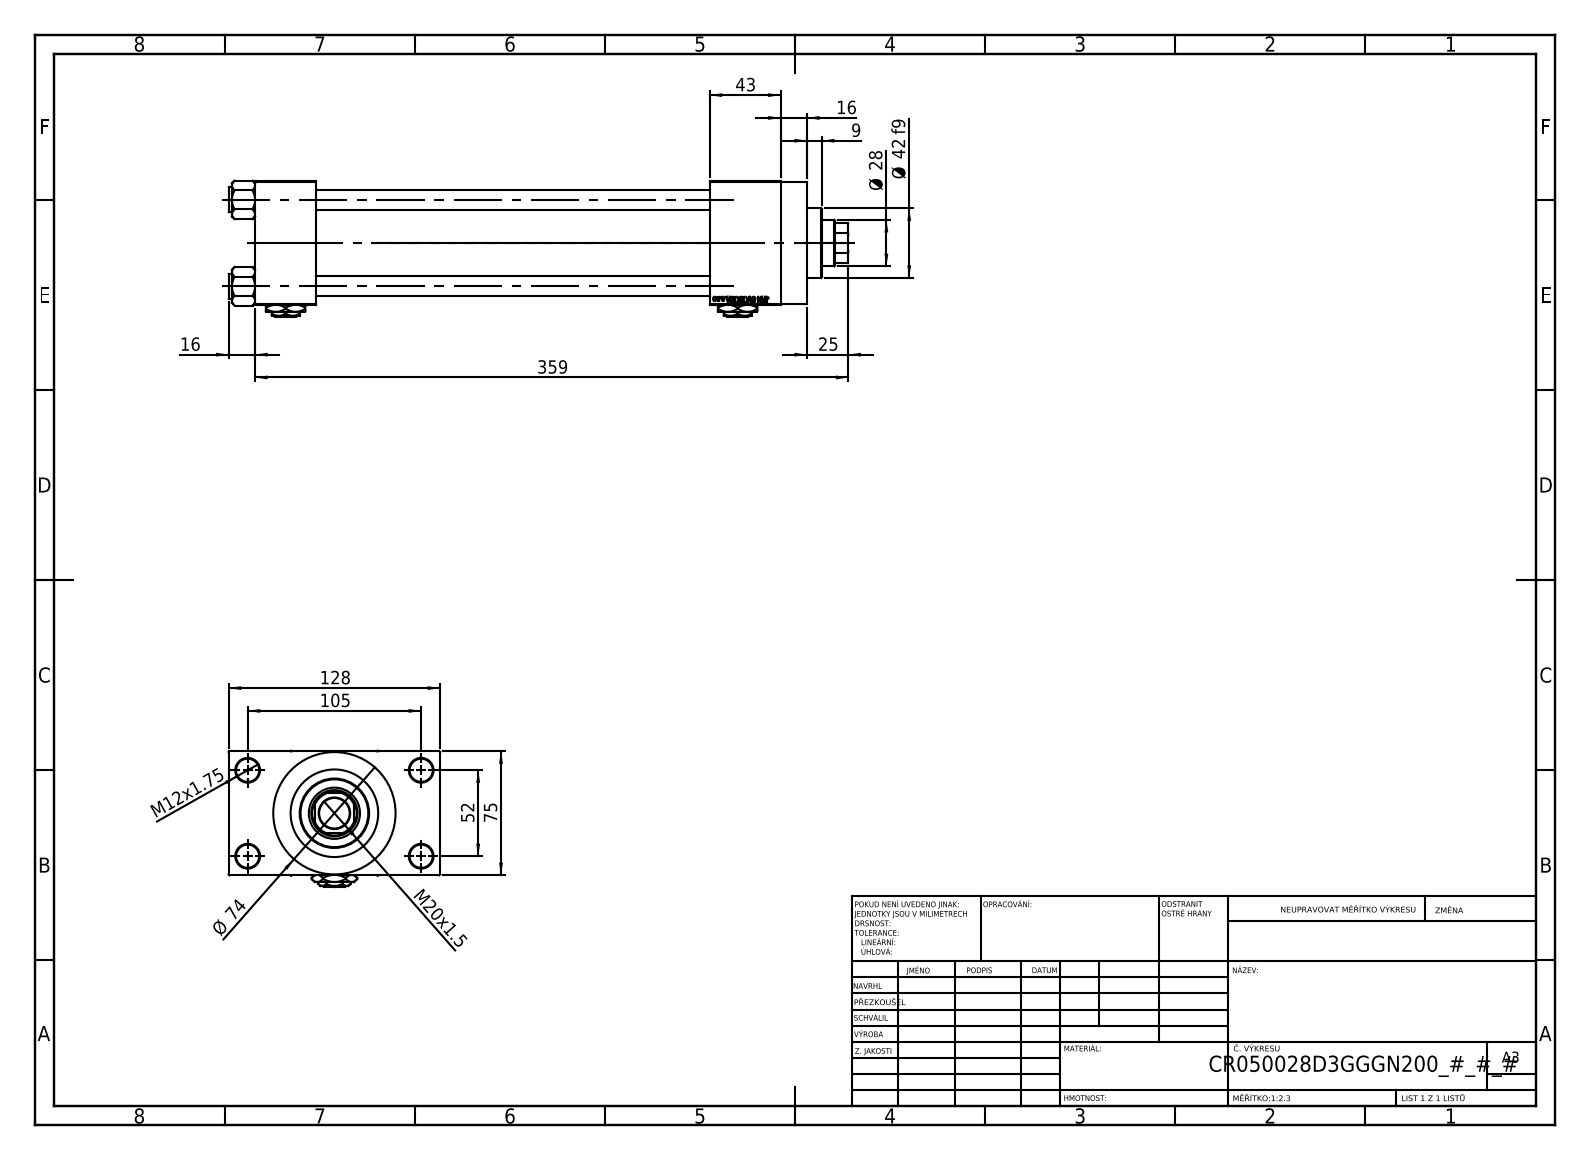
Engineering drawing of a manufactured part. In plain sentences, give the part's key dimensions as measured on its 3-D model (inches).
The part is named "NUT_M5_D; V215CR_D_Body; V215CR_VCP_D; V215CR_D_TYCINKA (+2 more)". Its 3-D file was written by "SolidWorks 2019 (CONFIG_CONTROL_DESIGN)". It is 13 solids with 1205 faces: 545 planar, 100 cylindrical and 560 other. Overall it measures 14.764 by 5.039 by 3.239 inches. Its volume is 66.7 cubic inches and its surface area 427.8 square inches. Round holes: 4 of diameter 0.472, 4 of diameter 0.551, 2 of diameter 0.276, 2 of diameter 0.825, 2 of diameter 1.181, 1 of diameter 0.728, 1 of diameter 1.102, 1 of diameter 1.22, 1 of diameter 1.614, 1 of diameter 1.969, 1 of diameter 2.087. Round bosses or shafts: 4 of diameter 0.591, 1 of diameter 2.913, 1 of diameter 2.205, 1 of diameter 1.654. Partial cylindrical surfaces (rounded edges, fillets, slot ends): 1 of radius 0.531. The main face-to-face distances are 2.953, 9.37, 1.457, 10.827, 1.043, 3.996, 12.52, 11.063, 1.693, 0.63. The hole center spacings are 1.037, 1.456, 2.059, 2.3, 2.307, 3.096, 3.715, 2.047.
